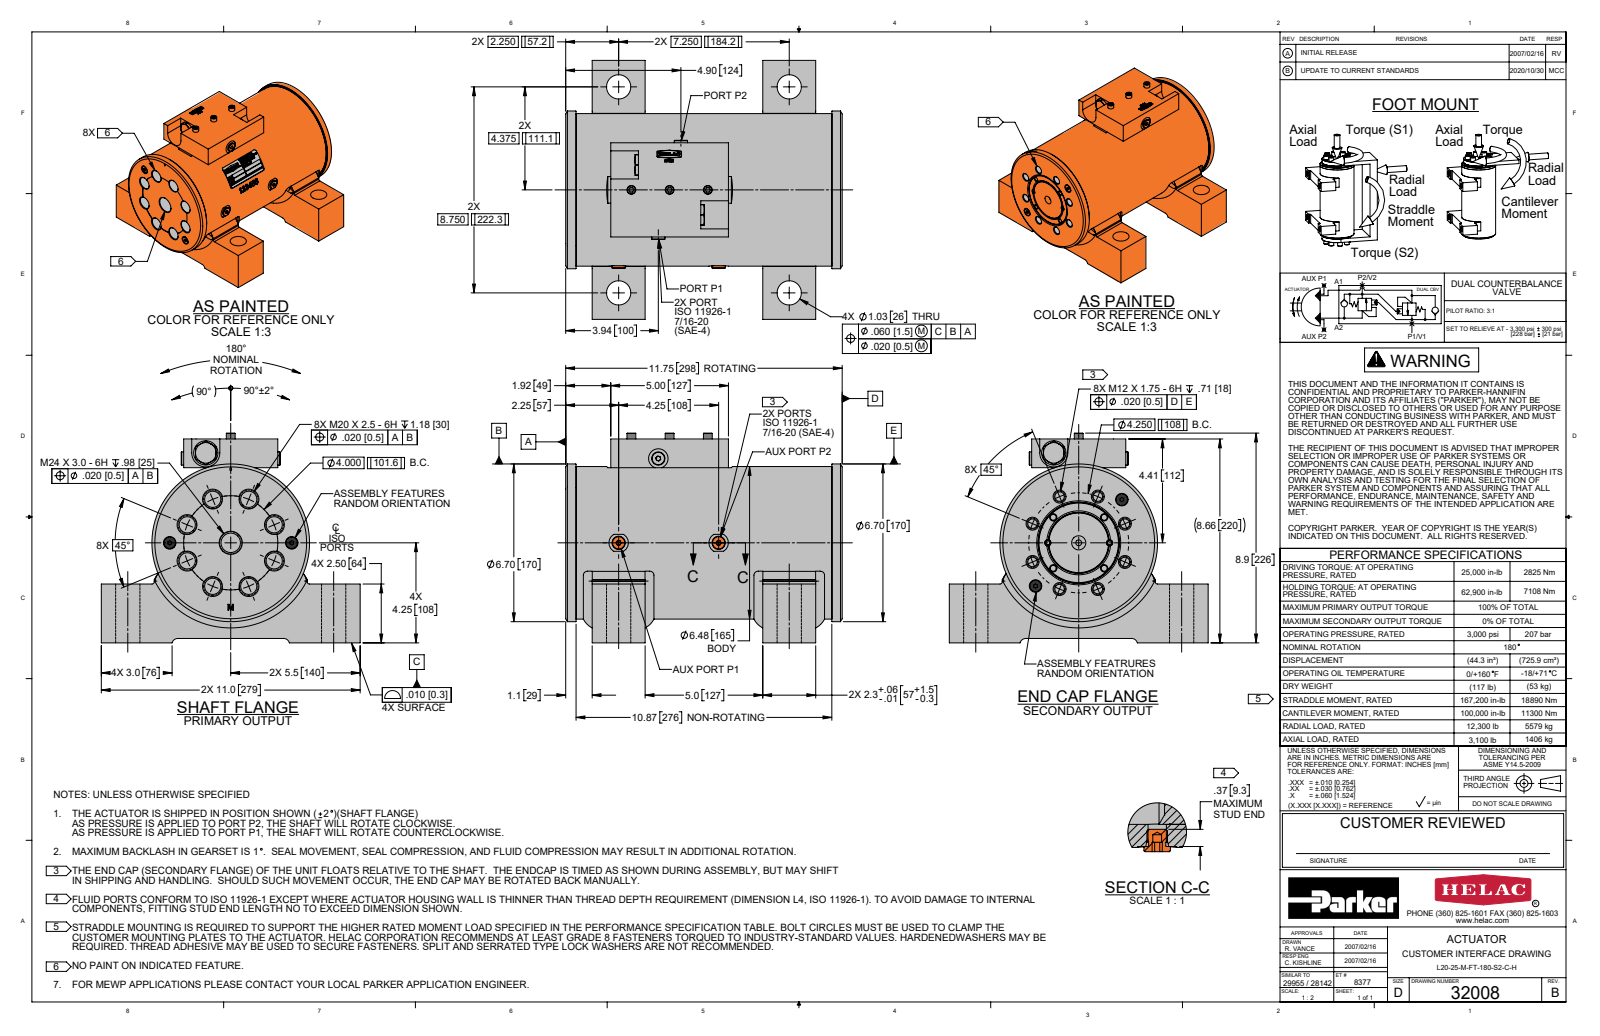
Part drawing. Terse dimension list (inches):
name: 32008D-CM.CYLH
written by: SolidWorks 2018 (AUTOMOTIVE_DESIGN)
unit: in
bodies: 25 solids, 1785 faces (488 planar, 614 cylindrical, 683 other)
size: 11.75 × 11 × 8.91
volume: 488.6 in³; area: 899.4 in²
holes: 8× ⌀0.402, 8× ⌀0.472, 8× ⌀0.689, 8× ⌀0.787, 7× ⌀0.25, 6× ⌀1.031, 5× ⌀0.266, 4× ⌀0.187, 2× ⌀0.19, 2× ⌀0.201, 2× ⌀0.202, 2× ⌀0.378
bosses: 5× ⌀0.25, 4× ⌀0.563, 4× ⌀0.365, 3× ⌀0.437, 3× ⌀0.375, 2× ⌀0.859, 2× ⌀0.781, 2× ⌀0.75
rounds: 12× R0.068, 4× R0.03, 4× R0.1, 2× R0.094, 2× R0.163, 2× R0.25, 2× R0.415, 2× R0.5
face distances: 0.44, 11.31, 9.5, 7.44, 5, 0.187, 1.125, 10.625, 7.253, 3.375
hole spacings: 2, 2.918, 3.811, 4.125, 2.125, 0.125, 0.828, 0.921
